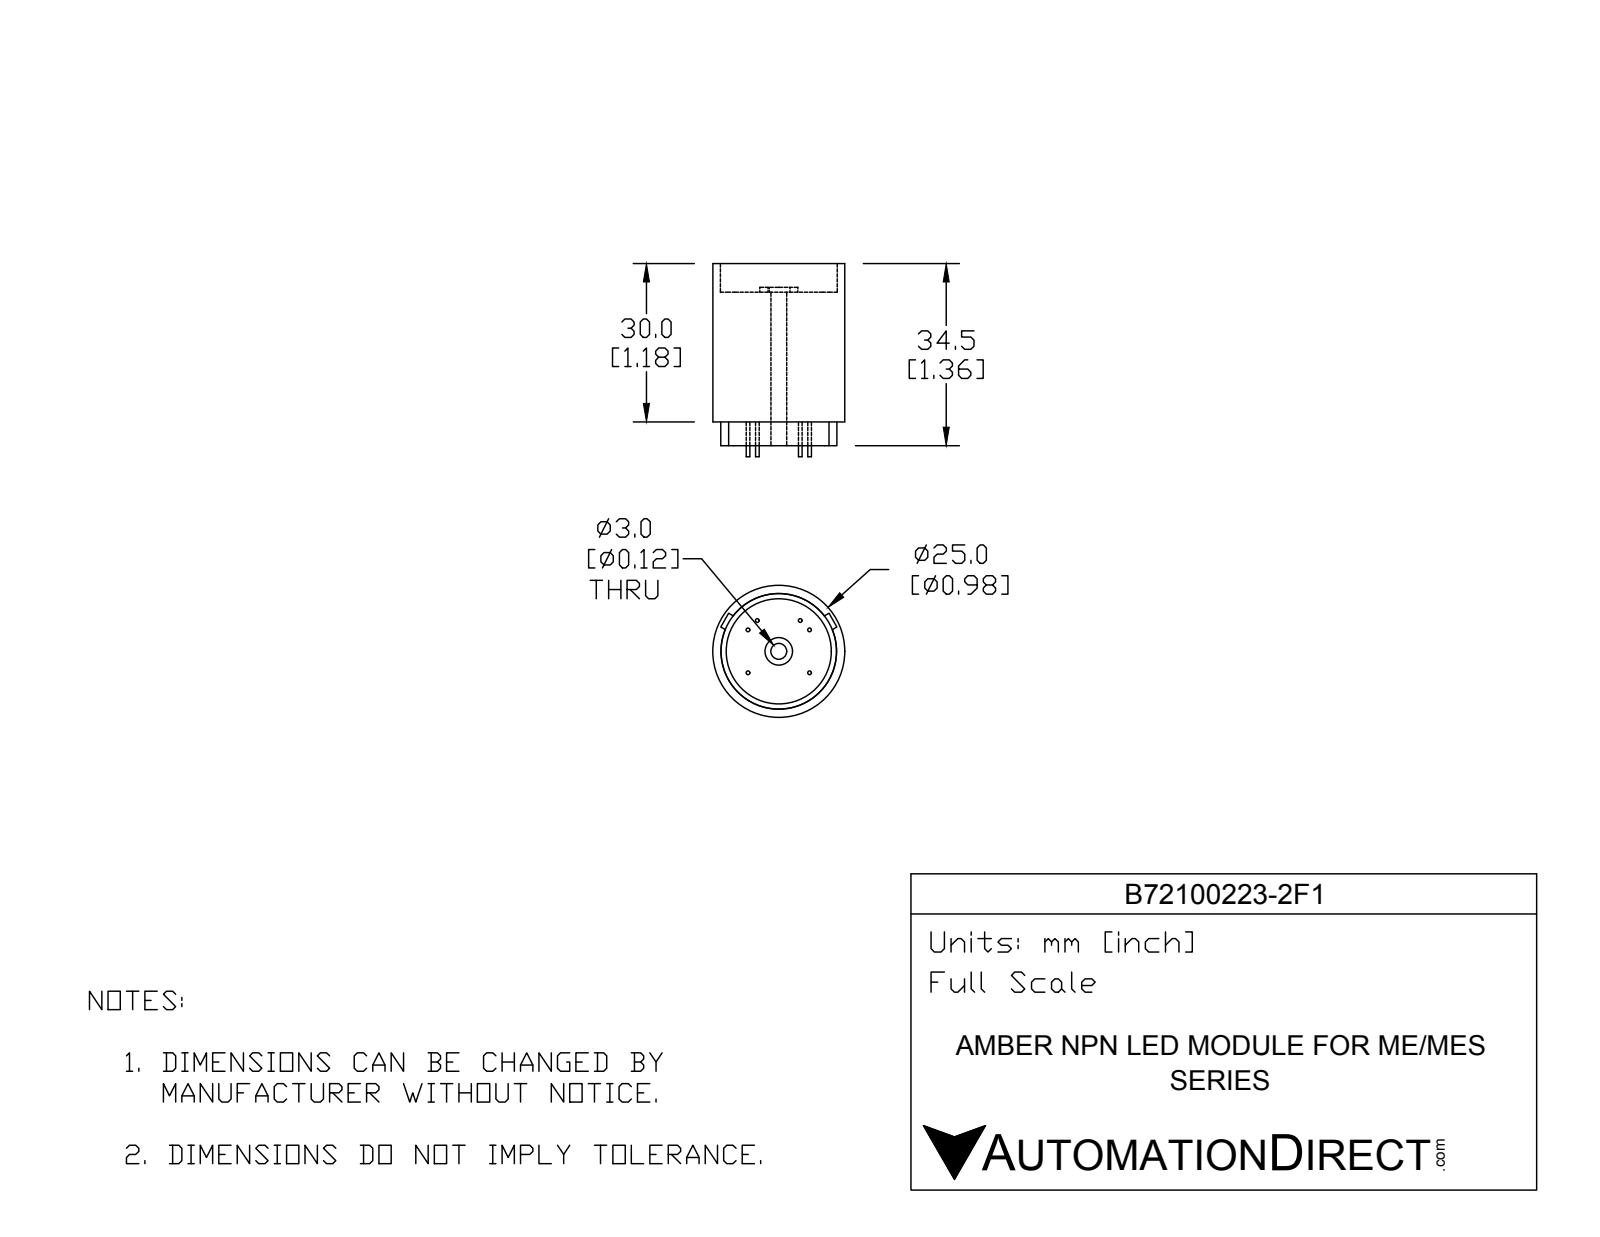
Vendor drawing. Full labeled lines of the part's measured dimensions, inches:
Part name (STEP PRODUCT): B72100223-2F1
STEP written by: SolidWorks 2016 (AUTOMOTIVE_DESIGN)
Units: inches
Bodies: 9 solids, 69 faces (36 planar, 33 cylindrical, 0 other)
Overall size (bounding box): 1.441 × 0.984 × 0.984
Volume: 0.791 in³ · Surface area: 7.57 in²
Round holes (diameter × count): ⌀0.118 ×1, ⌀0.166 ×1, ⌀0.783 ×1, ⌀0.846 ×1
Round bosses / shafts (diameter × count): ⌀0.028 ×6, ⌀0.984 ×1, ⌀0.862 ×1, ⌀0.284 ×1, ⌀0.205 ×1
Main face-to-face distances: 0.967, 1.181, 0.214, 0.177, 1.144, 1.358, 1.004, 0.037, 0.12, 0.122
